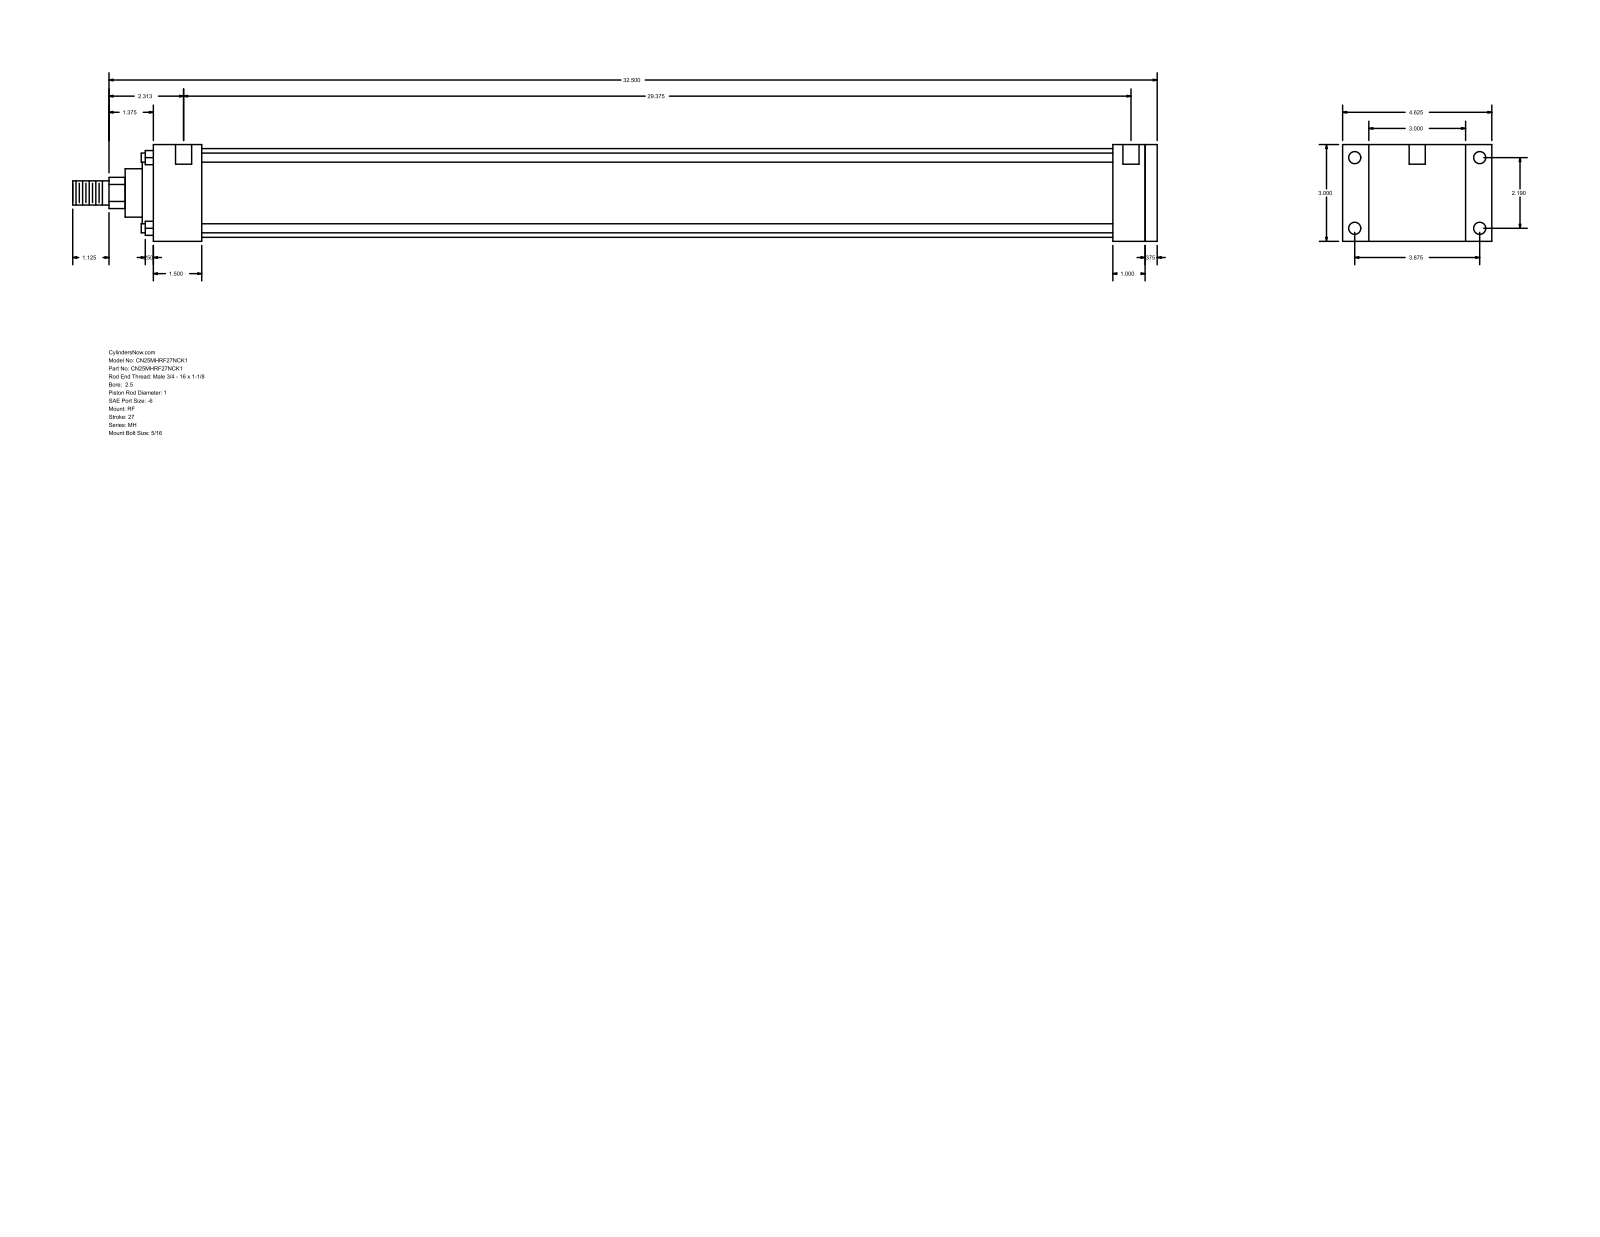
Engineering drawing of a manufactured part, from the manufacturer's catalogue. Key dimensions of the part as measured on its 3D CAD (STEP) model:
Part name (STEP PRODUCT): MH_RF__0250_1
STEP written by: GSSL Pune (CONFIG_CONTROL_DESIGN)
Units: millimetres
Bodies: 0 solids, 94 faces (65 planar, 29 cylindrical, 0 other)
Overall size (bounding box): 854.08 × 117.47 × 76.2
Round holes (diameter × count): ⌀5.56 ×4, ⌀9.53 ×4, ⌀12.7 ×2
Round bosses / shafts (diameter × count): ⌀7.14 ×4, ⌀69.85 ×1, ⌀60.33 ×1, ⌀38.1 ×1, ⌀25.4 ×1, ⌀19.05 ×1
Partial cylindrical surfaces — rounded edges, fillets, slot ends (radius × count): R12.29 ×1
Main face-to-face distances: 76.2, 9.52, 790.58, 781.06, 25.4, 34.92, 755.66, 38.11, 717.55, 742.95
Hole centre spacings: 55.62, 98.42, 113.05, 754.06, 3.18, 4.76, 746.12, 749.3
